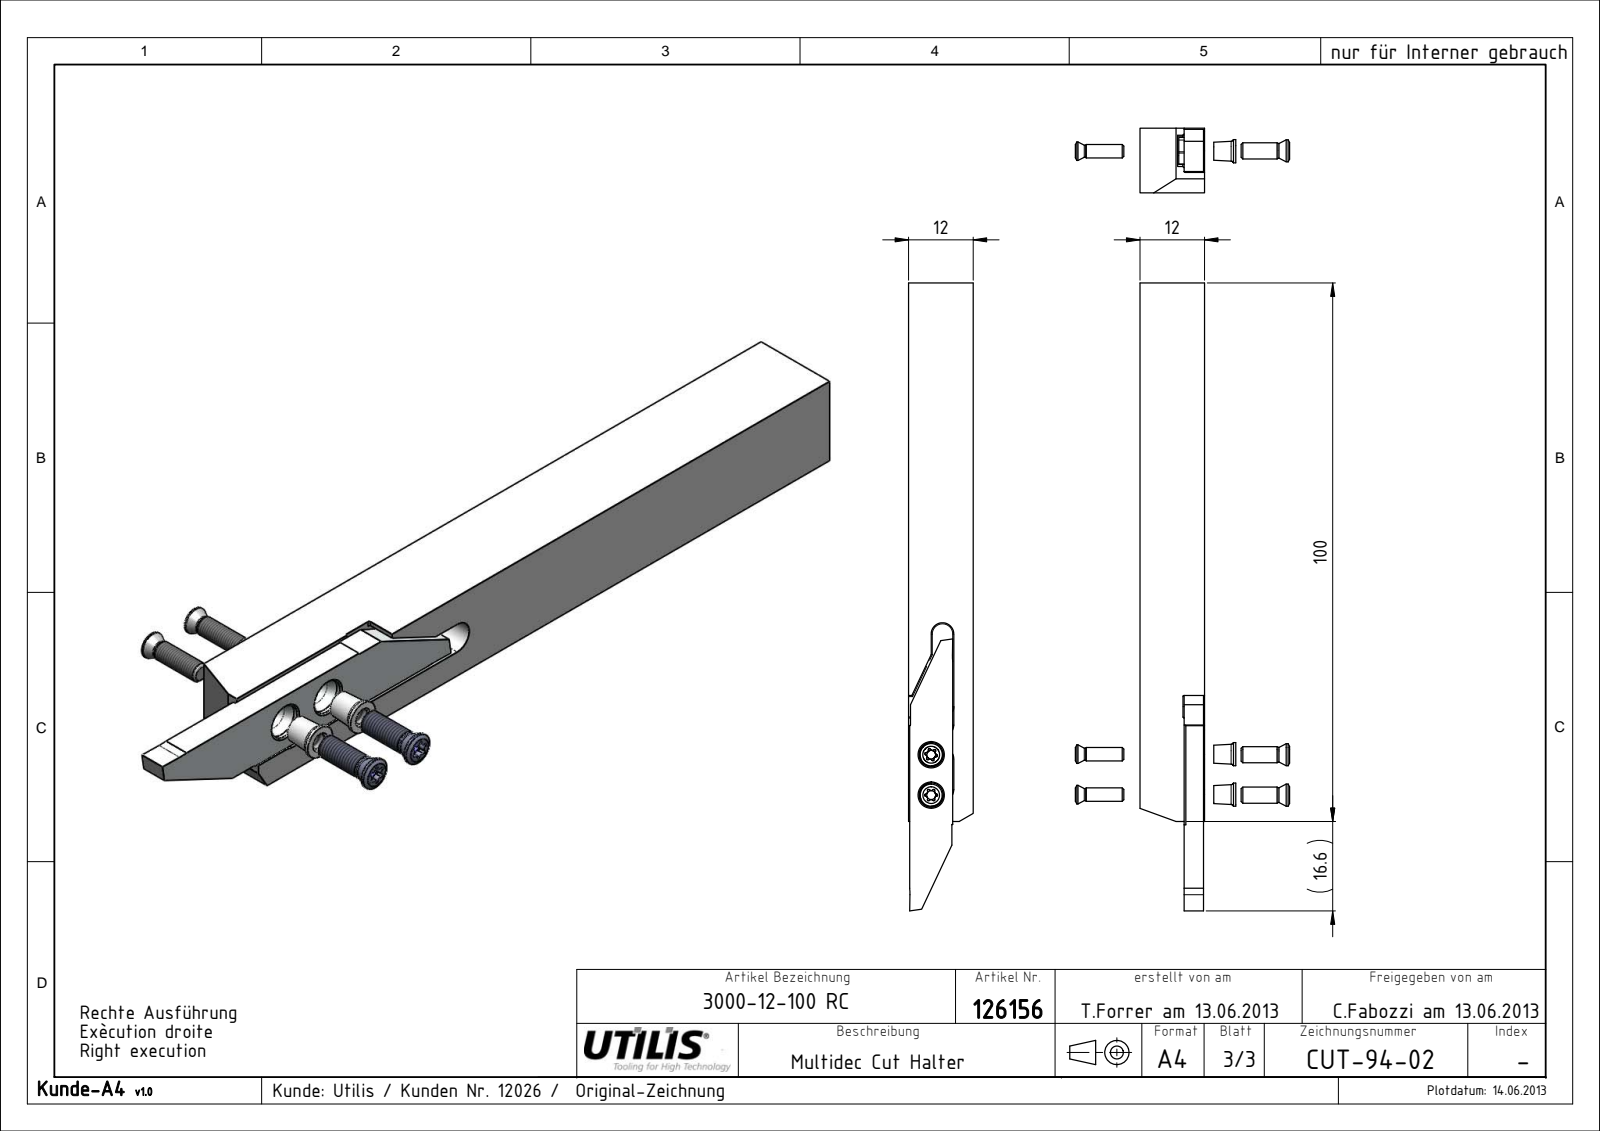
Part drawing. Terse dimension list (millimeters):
name: CUT-3000 R-L Kunde Lang_Lang; CUT-93-Kunde_3000-12-100 R; CUT-93-03; MSP-16_M3x7.3 T08
written by: SolidWorks 2013 (CONFIG_CONTROL_DESIGN)
unit: mm
bodies: 4 solids, 137 faces (42 planar, 55 cylindrical, 40 other)
size: 116.5 × 12 × 12
volume: 14 412 mm³; area: 6 499 mm²
holes: 2× ⌀2.5, 2× ⌀3.55
bosses: 2× ⌀4.1, 2× ⌀3
rounds: 12× R0.2, 12× R0.45, 4× R2.1, 2× R0.15, 2× R10
face distances: 12, 3.8, 8.2, 11.8, 3.6, 3.88, 8.12, 11.88, 8, 3.55
hole spacings: 7.5
